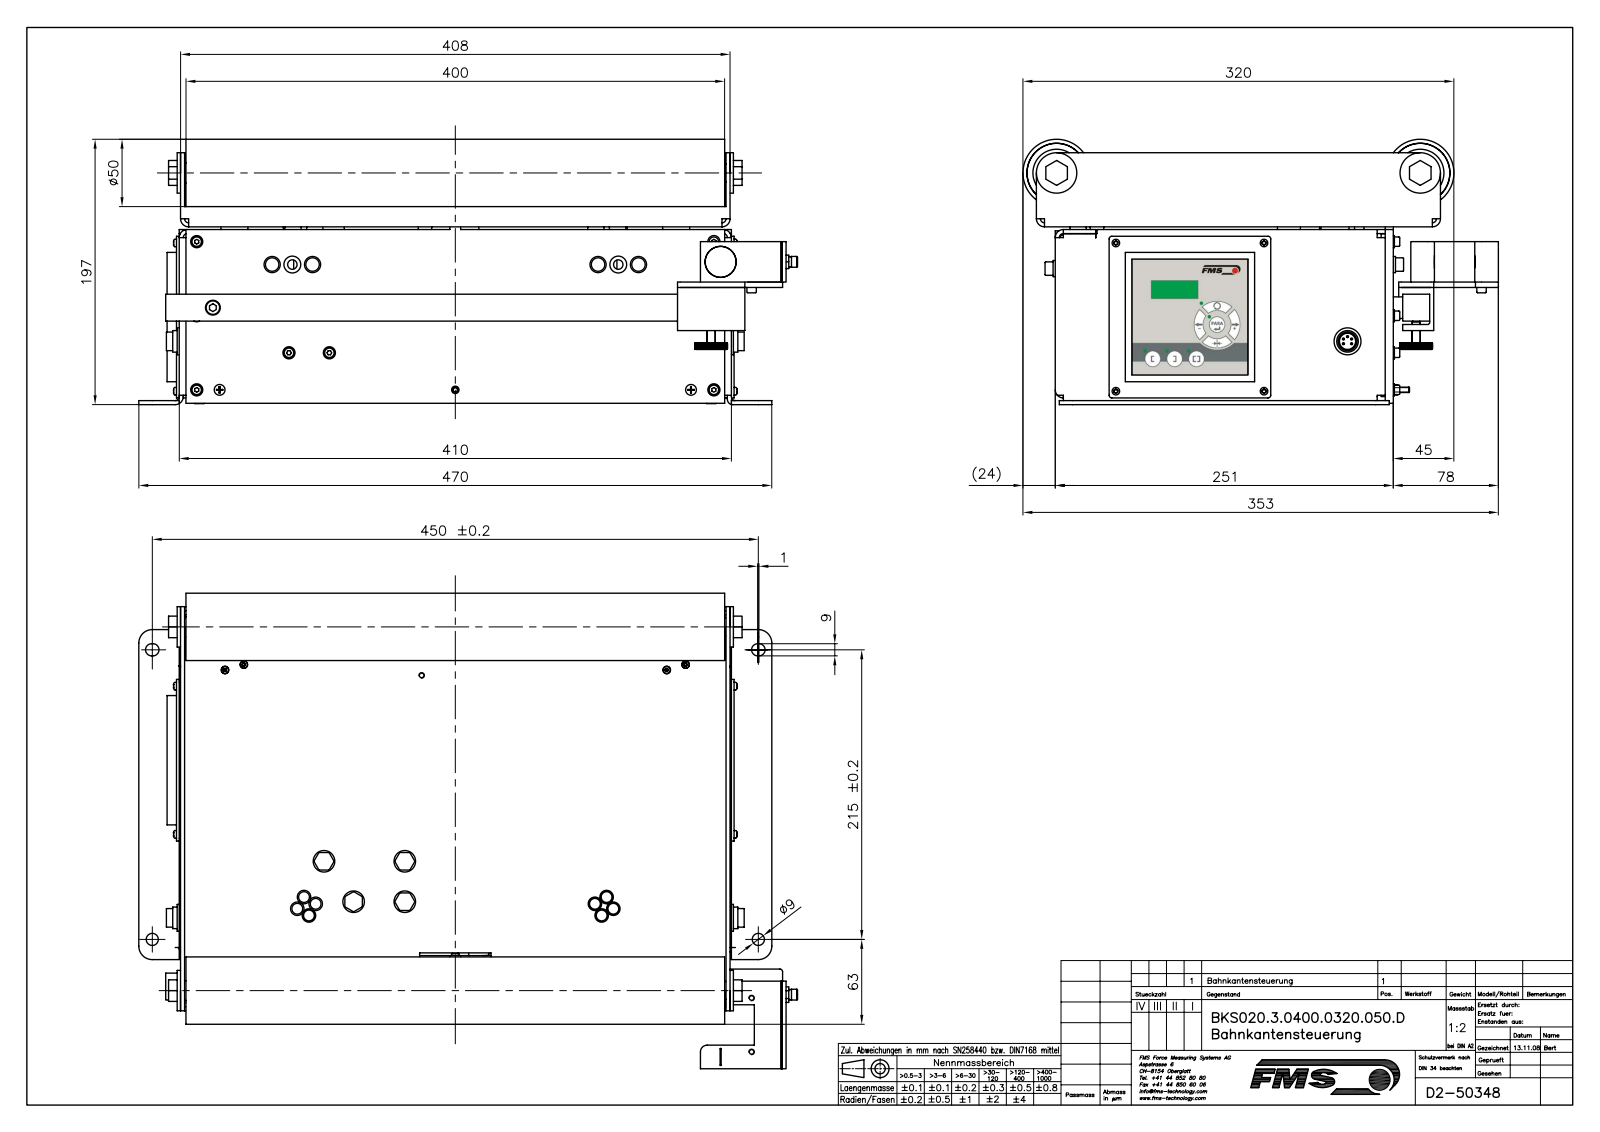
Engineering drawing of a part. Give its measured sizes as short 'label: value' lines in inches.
name: K50348; K0601245; K0601244; TEIL1 (+8 more)
written by: Mechanical Desktop 2007 (CONFIG_CONTROL_DESIGN)
unit: in
bodies: 169 solids, 6004 faces (3677 planar, 1851 cylindrical, 476 other)
size: 19.256 × 13.898 × 7.756
volume: 157.4 in³; area: 2 500 in²
holes: 30× ⌀0.118, 14× ⌀0.169, 13× ⌀0.135, 12× ⌀0.126, 12× ⌀0.252, 8× ⌀0.087, 8× ⌀0.102, 8× ⌀0.209, 7× ⌀0.138, 6× ⌀0.236, 6× ⌀0.331, 4× ⌀0.039
bosses: 22× ⌀0.394, 18× ⌀0.157, 15× ⌀0.315, 15× ⌀0.236, 12× ⌀0.472, 10× ⌀0.276, 8× ⌀0.354, 8× ⌀0.197
rounds: 48× R0.013, 29× R0.039, 24× R0.01, 24× R0.022, 24× R0.079, 20× R0.008, 19× R0.01, 14× R0.118
face distances: 0.118, 0.039, 5, 5.118, 0.079, 5.039, 5.157, 0.197, 0.236, 0.157
hole spacings: 0.394, 3.287, 3.836, 3.853, 4.331, 8.506, 0.591, 3.268
